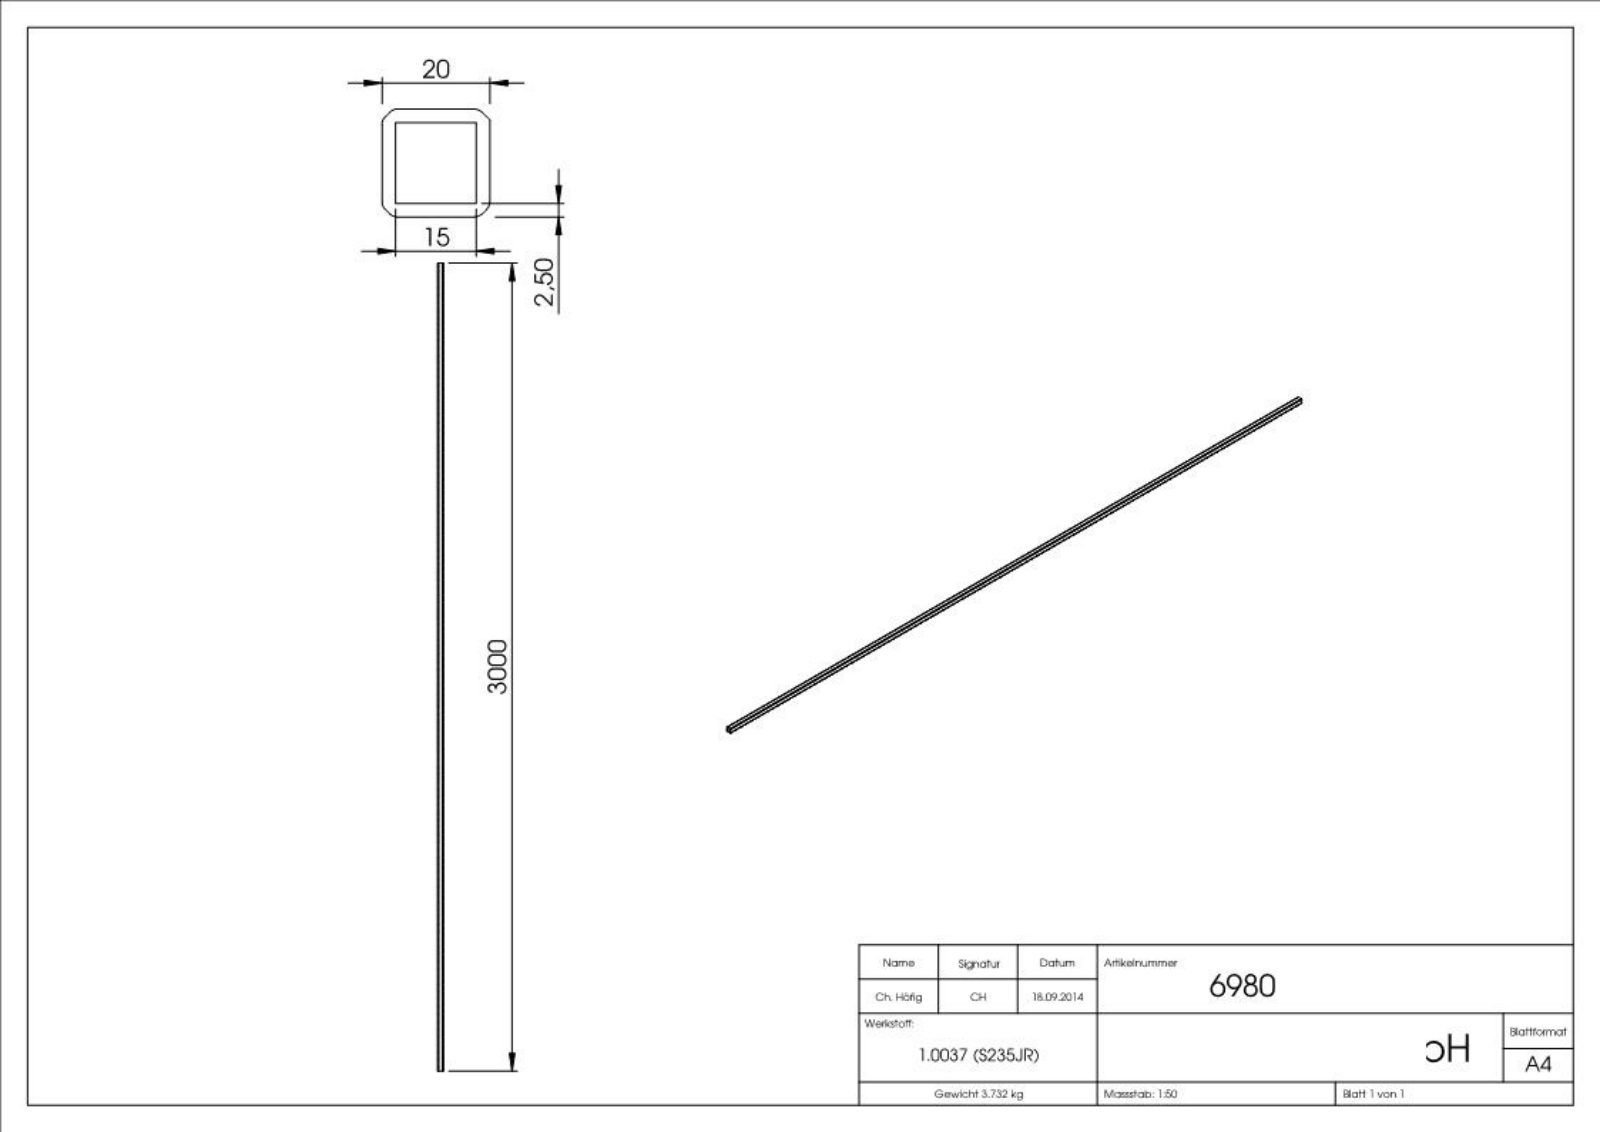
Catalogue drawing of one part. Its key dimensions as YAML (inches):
part_name: "6980"
step_written_by: "SolidWorks 2018 (CONFIG_CONTROL_DESIGN)"
units: inches
bodies: {solids: 1, faces: 2394, planar: 92, cylindrical: 1106, other: 1196}
overall_size: [118.11, 0.787, 0.787]
volume: 24.56
surface_area: 632.8
partial_cylinders:
  - {radius: 0.039, count: 4}
  - {radius: 0.118, count: 4}
face_to_face_distances: [0.079, 0.709, 0.787, 0.63, 118.11, 98.425, 19.685, 0.075, 0.634, 0.713]
